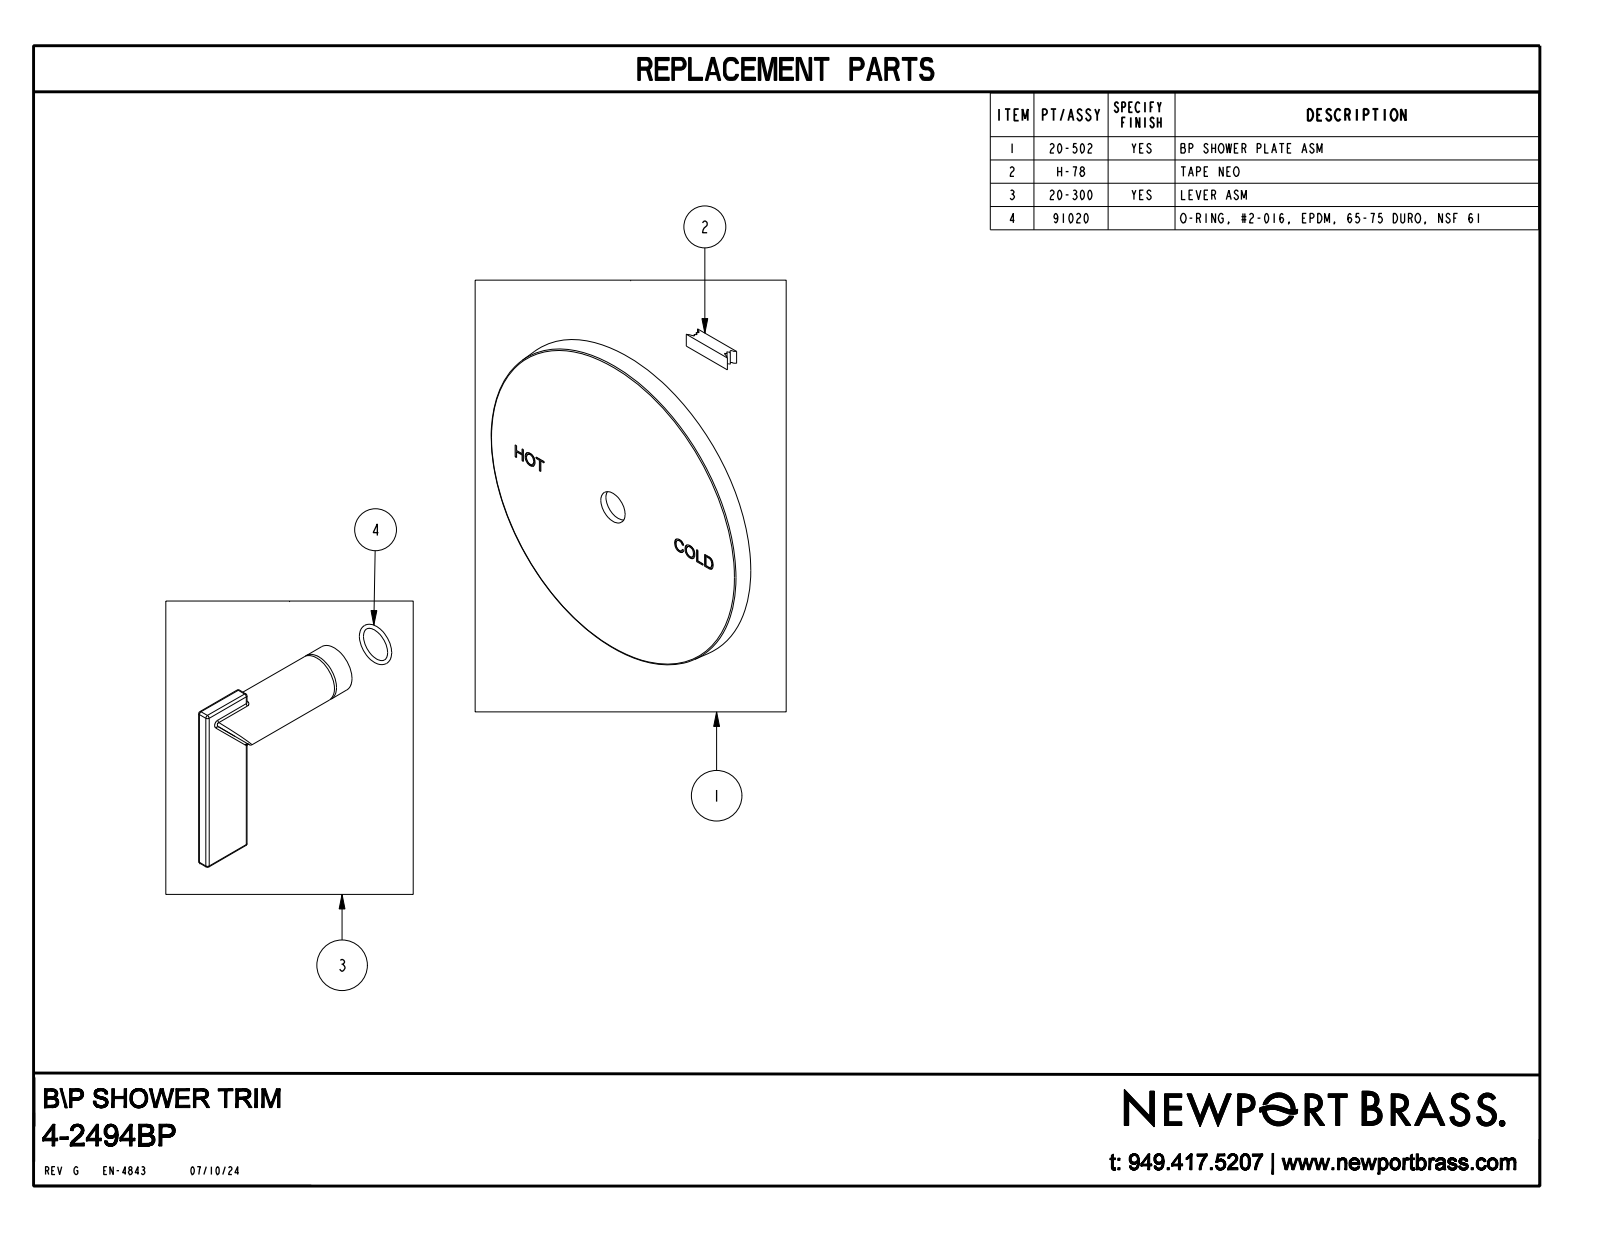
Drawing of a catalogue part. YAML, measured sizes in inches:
part_name: "4-2494BP"
step_written_by: "CREO PARAMETRIC BY PTC INC, 2018400 (CONFIG_CONTROL_DESIGN)"
units: inches
bodies: {solids: 1, faces: 183, planar: 57, cylindrical: 24, other: 102}
overall_size: [6, 6, 3.55]
volume: 11.96
surface_area: 76.83
round_bosses_or_shafts:
  - {diameter: 0.86, count: 1}
  - {diameter: 0.68, count: 1}
partial_cylinders:
  - {radius: 0.04, count: 16}
face_to_face_distances: [0.35, 0.236, 3.55, 3.2, 2.566, 2.216, 0.984, 0.726, 0.376, 1.84]
